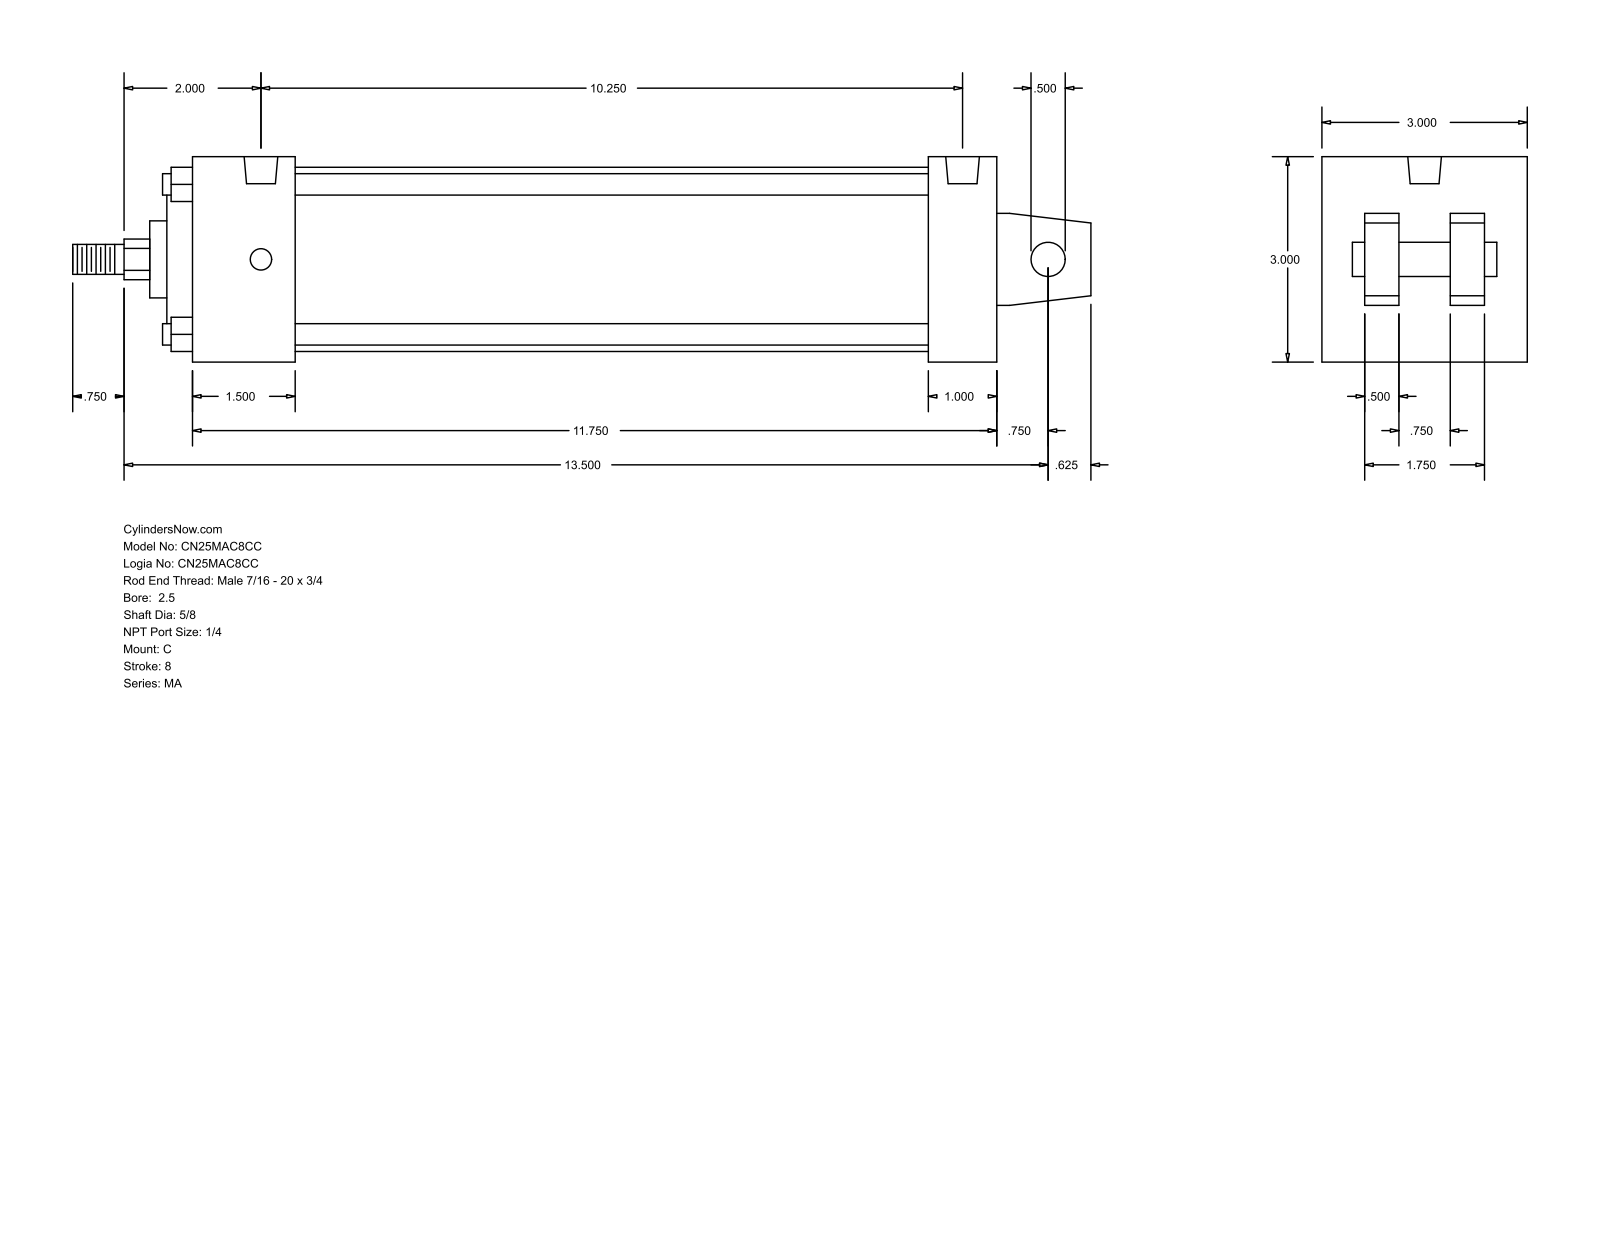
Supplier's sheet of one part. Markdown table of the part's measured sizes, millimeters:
| quantity | value |
| --- | --- |
| part name | MA_C__0250_0.625 |
| STEP written by | GSSL Pune (CONFIG_CONTROL_DESIGN) |
| units | millimeters |
| bodies | 0 solids, 105 faces (77 planar, 28 cylindrical, 0 other) |
| overall size | 377.82 × 76.2 × 76.2 |
| round holes (diameter × count) | 7.94 × 4, 12.49 × 2 |
| round bosses / shafts (diameter × count) | 7.94 × 4, 68.33 × 1, 50.8 × 1, 28.57 × 1, 15.88 × 1, 12.7 × 1, 11.11 × 1 |
| partial cylindrical surfaces (radius × count) | 7.54 × 1 |
| main face-to-face distances | 76.2, 298.45, 12.7, 15.87, 47.63, 25.4, 38.1, 273.05, 234.95, 260.35 |
| hole center spacings | 260.35 |
